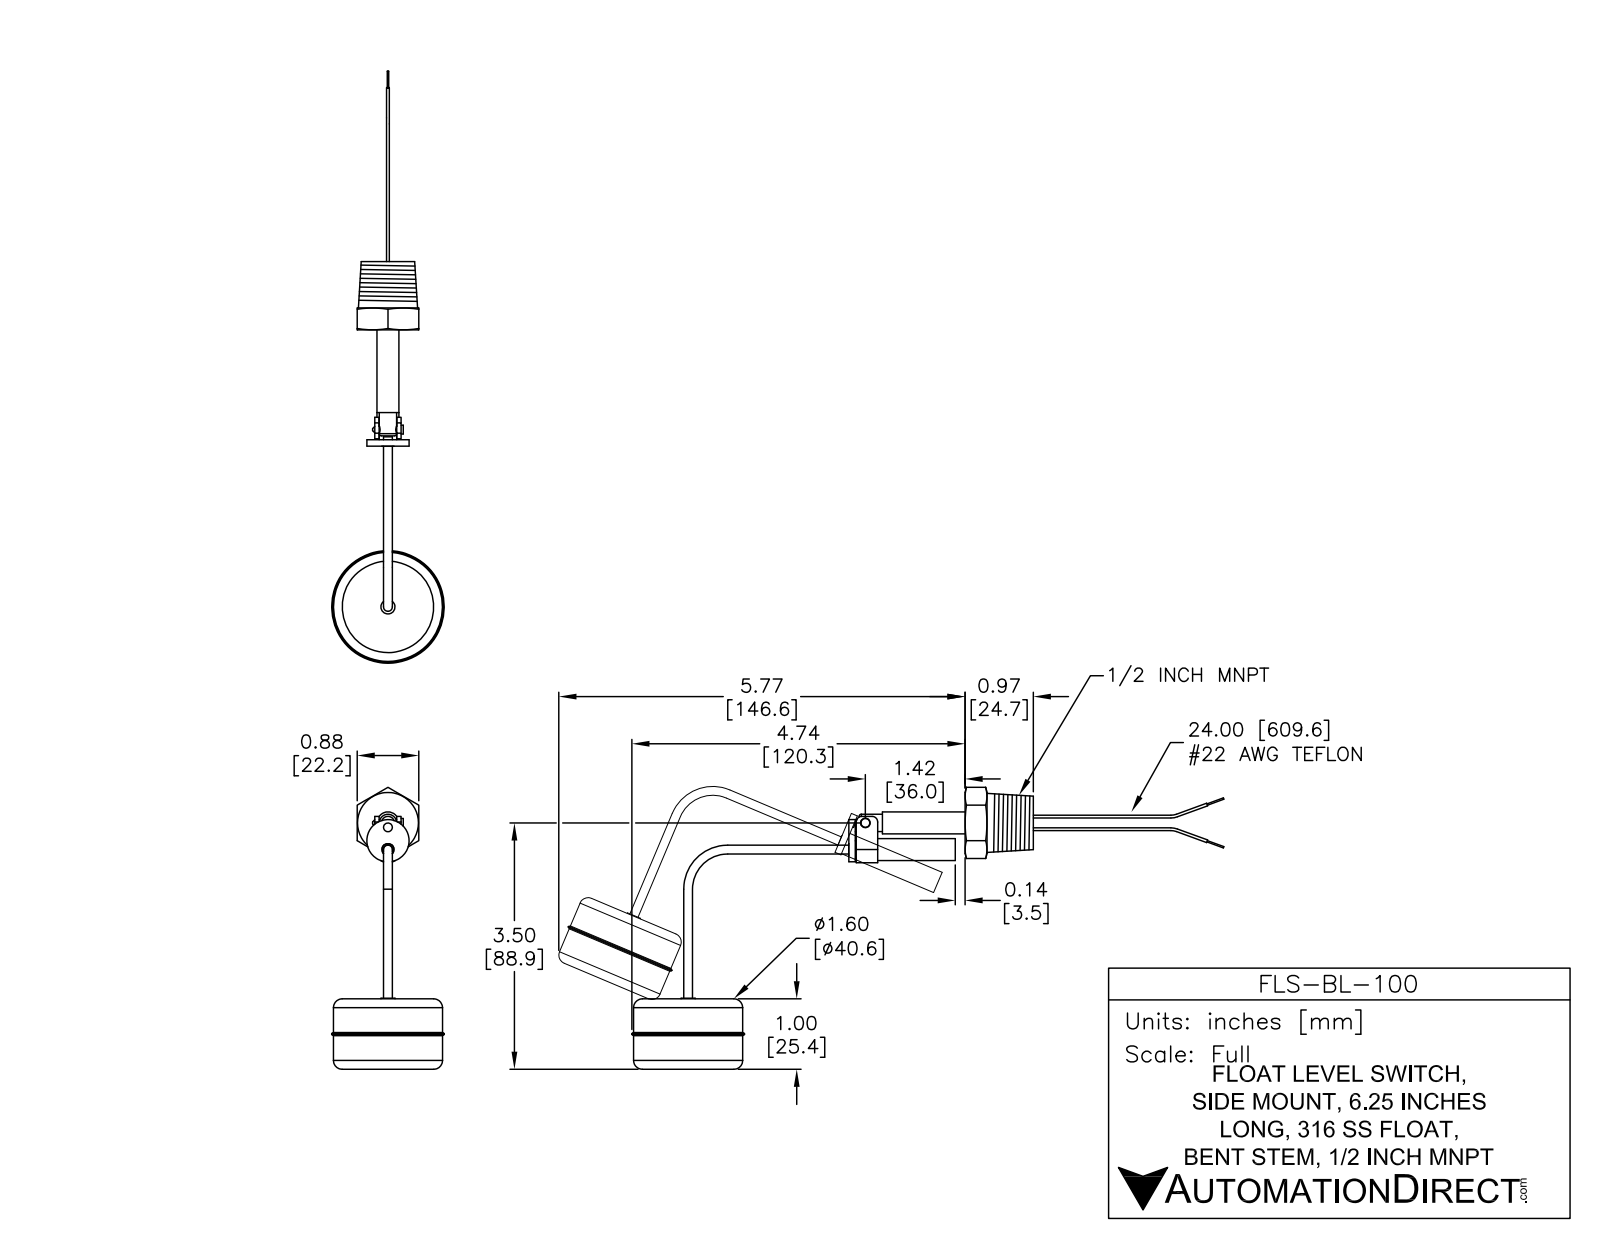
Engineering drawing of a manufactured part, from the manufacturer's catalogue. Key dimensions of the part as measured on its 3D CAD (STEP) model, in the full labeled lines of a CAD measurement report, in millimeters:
Part name (STEP PRODUCT): FLS-BL-100
STEP written by: SolidWorks 2013 (AUTOMOTIVE_DESIGN)
Units: millimetres
Bodies: 8 solids, 135 faces (45 planar, 60 cylindrical, 30 other)
Overall size (bounding box): 214.1 × 101.7 × 40.6
Volume: 43 210 mm³ · Surface area: 14 460 mm²
Round holes (diameter × count): ⌀2.5 ×1, ⌀2.7 ×1, ⌀3.2 ×1, ⌀3.4 ×1, ⌀3.4 ×1, ⌀6.5 ×1
Round bosses / shafts (diameter × count): ⌀3.2 ×4, ⌀1 ×4, ⌀7.9 ×2, ⌀0.5 ×2, ⌀40.6 ×1, ⌀39.4 ×1, ⌀15.2 ×1, ⌀6.4 ×1
Partial cylindrical surfaces — rounded edges, fillets, slot ends (radius × count): R2 ×2, R3.2 ×1, R4.7 ×1
Main face-to-face distances: 25.4, 8, 22.2, 16.7, 24.6, 68.4, 51.7, 43.8, 70.7, 54.1
Hole centre spacings: 1.6, 8.3, 9.9
